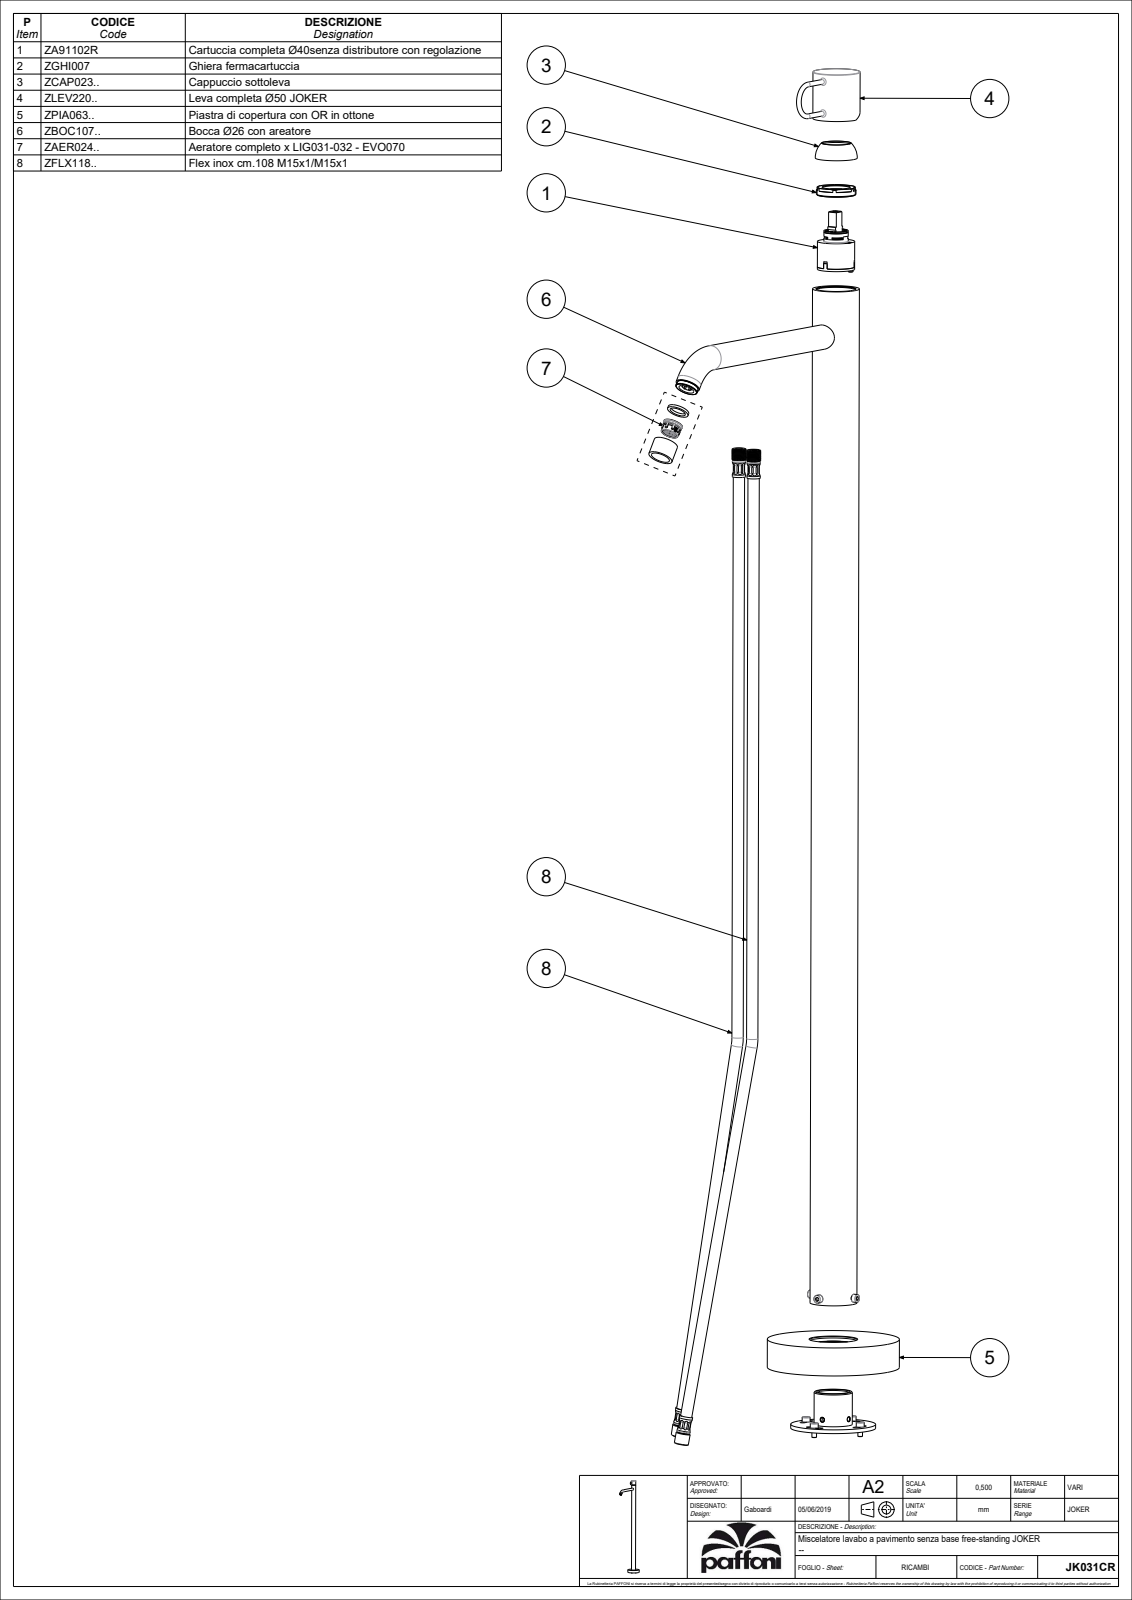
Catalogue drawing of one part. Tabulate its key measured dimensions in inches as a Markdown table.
| quantity | value |
| --- | --- |
| part name | JK031CR |
| STEP written by | CREO PARAMETRIC BY PTC INC, 2020044 (CONFIG_CONTROL_DESIGN) |
| units | inches |
| bodies | 3 solids, 1760 faces (1618 planar, 80 cylindrical, 62 other) |
| overall size | 44.95 × 14.346 × 5.512 |
| volume | 77.44 in³ |
| surface area | 643.9 in² |
| round holes (diameter × count) | 0.118 × 1, 0.13 × 1, 0.165 × 1, 0.177 × 1, 0.217 × 1, 0.669 × 1, 0.728 × 1, 0.787 × 1, 0.795 × 1, 0.811 × 1, 0.827 × 1, 0.835 × 1 |
| round bosses / shafts (diameter × count) | 1.024 × 2, 0.197 × 2, 5.512 × 1, 1.969 × 1, 1.957 × 1, 0.827 × 1, 0.768 × 1, 0.74 × 1 |
| partial cylindrical surfaces (radius × count) | 0.975 × 1 |
| main face-to-face distances | 1.181, 44.815, 43.634, 0.059, 0.02, 0.039, 0.098, 0.079, 0.398, 42.874 |
| hole center spacings | 2.925, 3.016 |
